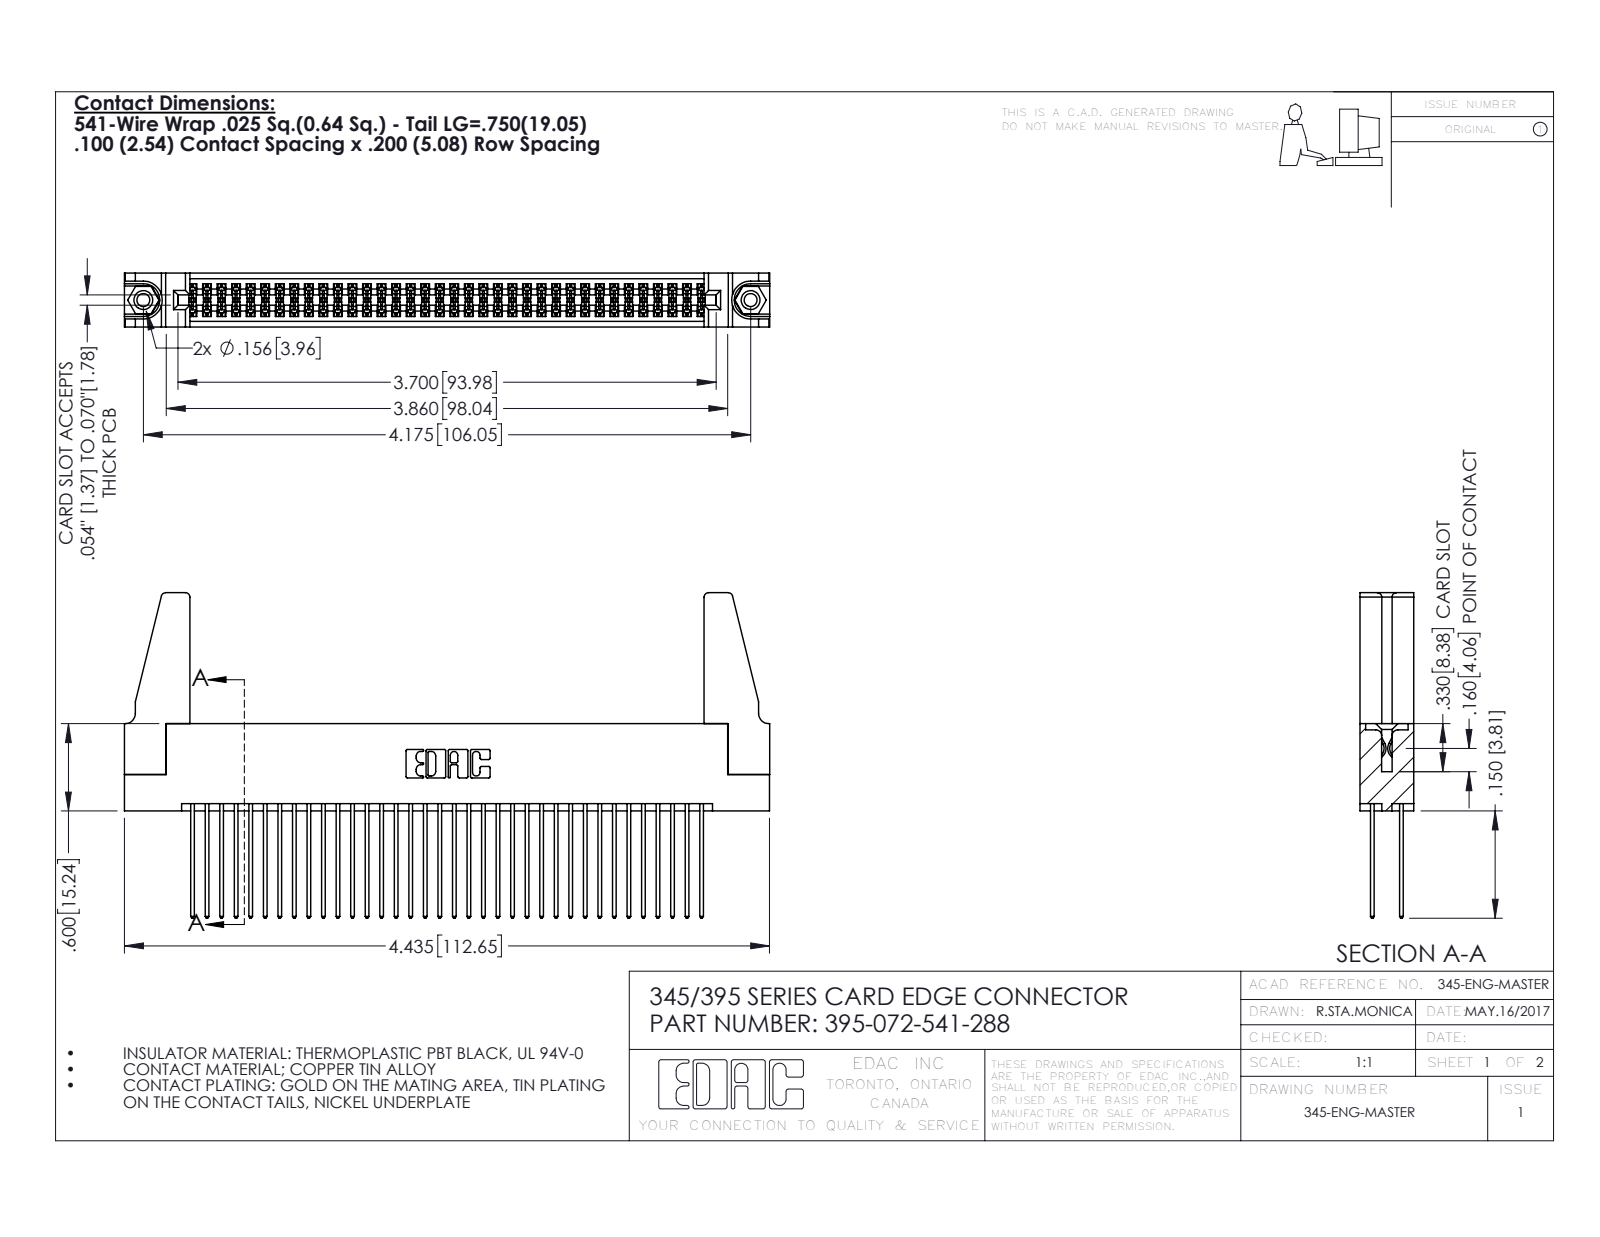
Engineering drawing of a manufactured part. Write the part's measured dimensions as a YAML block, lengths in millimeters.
part_name: "345 Part_Flush Mounting Lugs - 0.156 Dia-TH; 345-250-001_345-250-001-102; 345-292-001_345-293-141; 395-072-541-288 (+1 more)"
step_written_by: "SolidWorks 2016 (CONFIG_CONTROL_DESIGN)"
units: millimeters
bodies: {solids: 77, faces: 3850, planar: 2528, cylindrical: 1306, other: 16}
overall_size: [112.7, 56.8, 9.4]
volume: 14600
surface_area: 21660
round_holes:
  - {diameter: 2.3, count: 2}
  - {diameter: 3.2, count: 2}
  - {diameter: 4, count: 2}
  - {diameter: 1.6, count: 1}
round_bosses_or_shafts:
  - {diameter: 3.9, count: 2}
partial_cylinders:
  - {radius: 0.2, count: 108}
  - {radius: 0.3, count: 72}
  - {radius: 0.3, count: 22}
  - {radius: 0.8, count: 8}
  - {radius: 0.2, count: 6}
  - {radius: 0.8, count: 6}
  - {radius: 0.7, count: 3}
  - {radius: 0.4, count: 2}
face_to_face_distances: [1.8, 7.6, 5.1, 2.5, 6.9, 0.6, 9.4, 5.7, 4.4, 3.8]
hole_center_spacings: [6.9, 100.1, 106]
